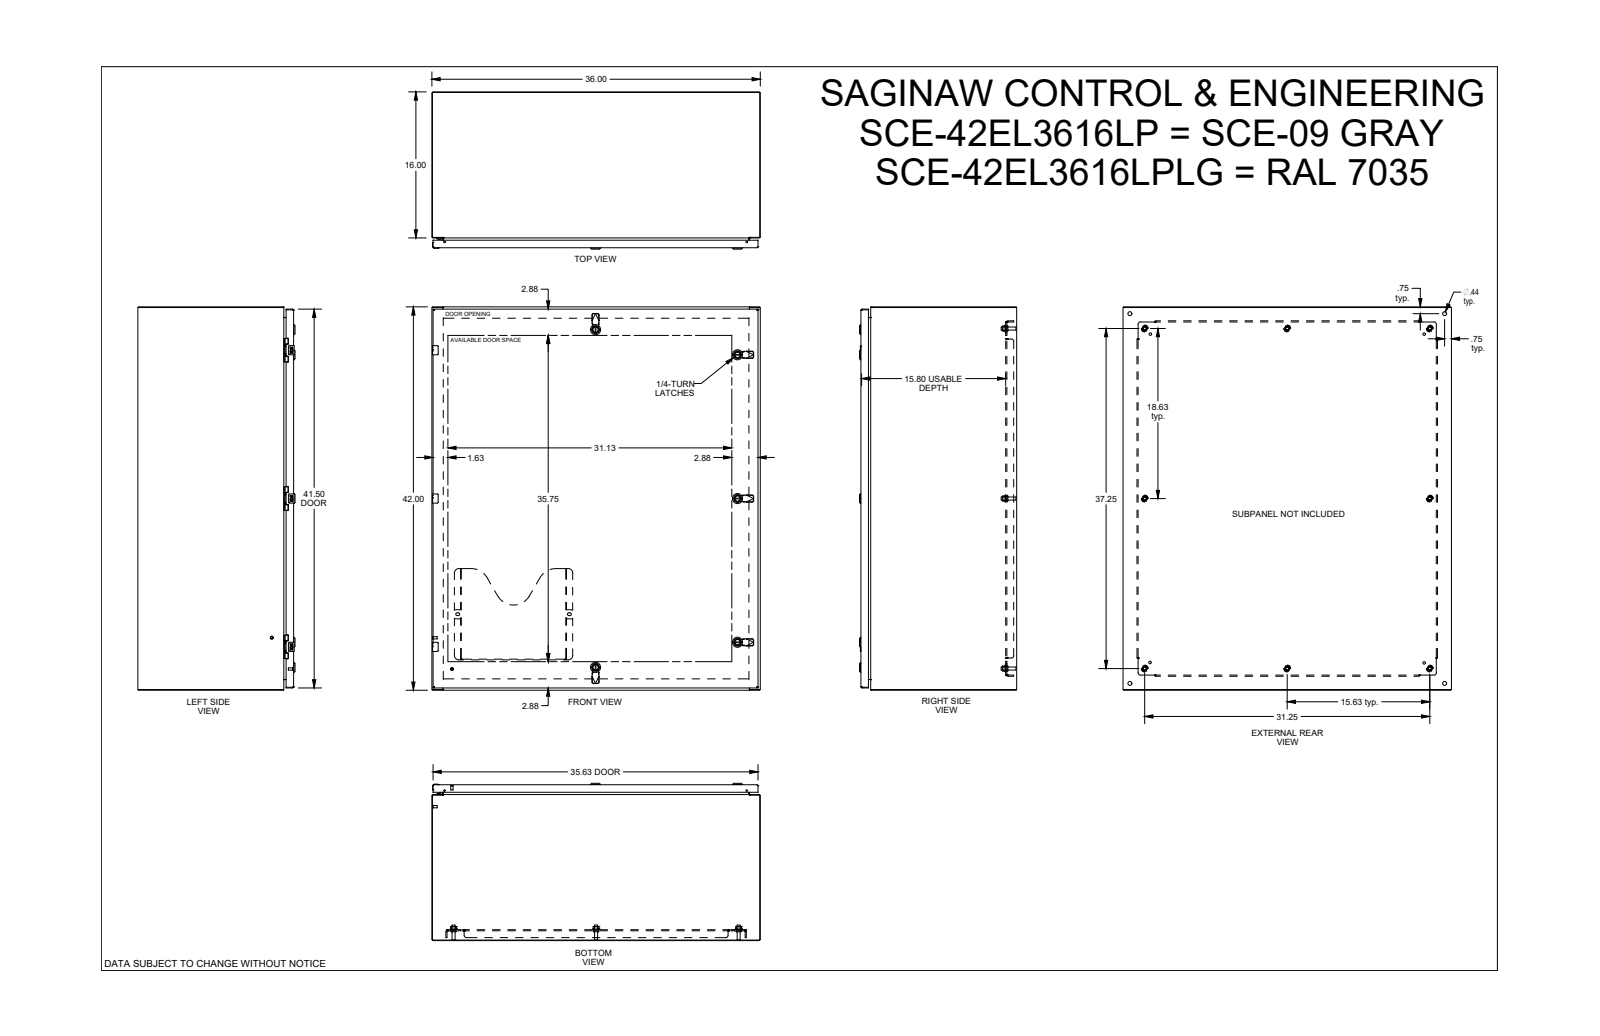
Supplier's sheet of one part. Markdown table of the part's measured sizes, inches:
| quantity | value |
| --- | --- |
| part name | SCE-42EL3616LP |
| STEP written by | SolidWorks 2019 (CONFIG_CONTROL_DESIGN) |
| units | inches |
| bodies | 0 solids, 4774 faces (2327 planar, 1328 cylindrical, 1119 other) |
| overall size | 42 × 36 × 17.23 |
| round holes (diameter × count) | 0.367 × 8, 0.5 × 8, 0.172 × 6, 0.205 × 6, 0.244 × 6, 0.266 × 6, 0.375 × 6, 0.197 × 5, 0.315 × 5, 0.394 × 5, 0.634 × 5, 0.281 × 4 |
| round bosses / shafts (diameter × count) | 0.17 × 9, 0.366 × 8, 0.332 × 8, 0.25 × 6, 0.24 × 6, 1.102 × 5, 0.866 × 5, 0.802 × 5 |
| partial cylindrical surfaces (radius × count) | 0.012 × 136, 0.01 × 52, 0.02 × 52, 0.015 × 32, 0.157 × 20, 0.04 × 17, 0.025 × 16, 0.1 × 16 |
| main face-to-face distances | 0.075, 0.075, 16.998, 16.923, 17.073, 16.998, 1.2, 15.873, 35.925, 1 |
| hole center spacings | 16.25, 0.985, 32.5, 0.02, 0.493, 0.494, 4.493, 15.265 |
